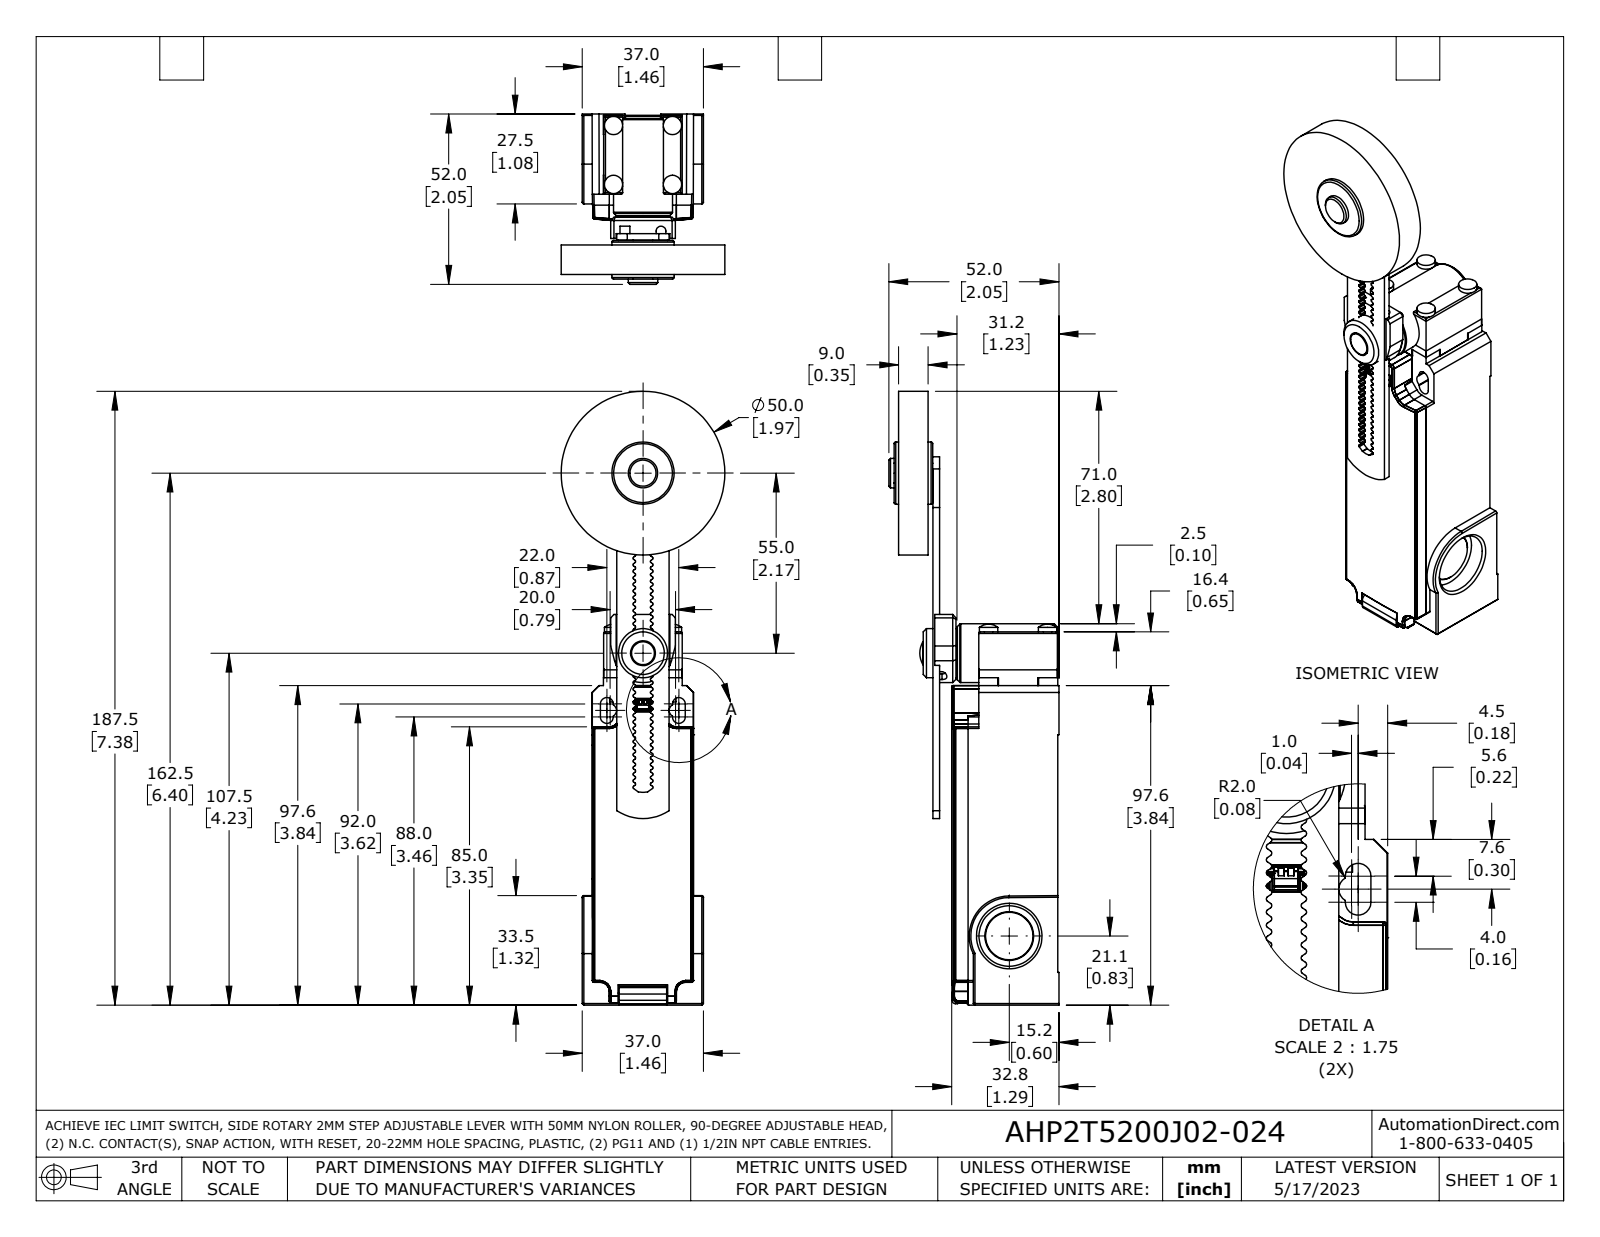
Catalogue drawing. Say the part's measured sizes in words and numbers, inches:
The part is named "AHP2T5200J02-024". Its 3-D file was written by "SolidWorks 2021 (AUTOMOTIVE_DESIGN)". It is 1 solid with 905 faces: 507 planar, 313 cylindrical and 85 other. Overall it measures 7.382 by 2.047 by 1.969 inches. Its volume is 7.654 cubic inches and its surface area 52.3 square inches. Round holes: 4 of diameter 0.091, 4 of diameter 0.118, 2 of diameter 0.728, 1 of diameter 0.299, 1 of diameter 0.86. Round bosses or shafts: 4 of diameter 0.22, 1 of diameter 1.969, 1 of diameter 0.748, 1 of diameter 0.709, 1 of diameter 0.591, 1 of diameter 0.354, 1 of diameter 0.276, 1 of diameter 0.236. Partial cylindrical surfaces (rounded edges, fillets, slot ends): 140 of radius 0.016, 41 of radius 0.012, 38 of radius 0.02, 6 of radius 0.008, 4 of radius 0.039, 4 of radius 0.118, 3 of radius 0.031, 2 of radius 0.079. The main face-to-face distances are 0.354, 1.559, 1.913, 0.059, 1.5, 0.236, 0.492, 0.138, 0.413, 0.079. The hole center spacings are 0.709, 0.431, 0.583, 1.002.
